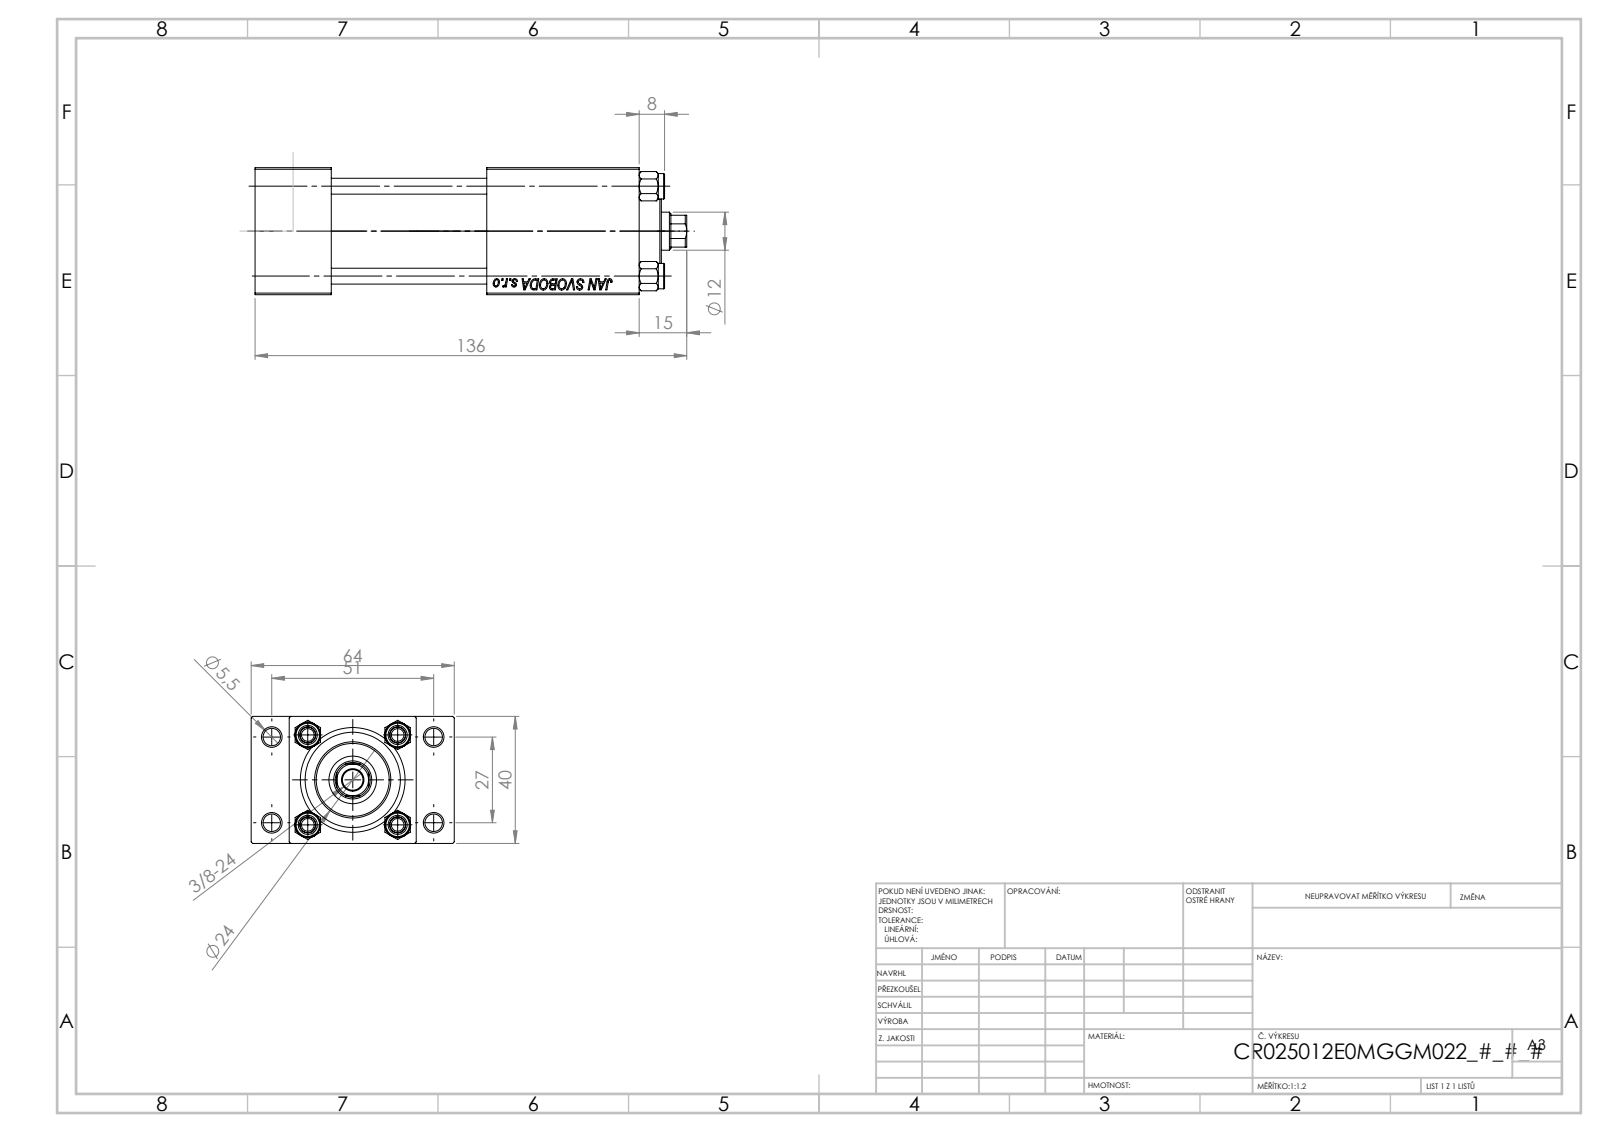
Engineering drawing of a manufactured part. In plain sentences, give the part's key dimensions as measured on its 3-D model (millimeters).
The part is named "V215CR_VCP_E; V215CR_E_Body; V215CR_TYCINKA_E; V215_VC_A (+1 more)". Its 3-D file was written by "SolidWorks 2019 (CONFIG_CONTROL_DESIGN)". It is 11 solids with 1136 faces: 497 planar, 87 cylindrical and 552 other. Overall it measures 136 by 64 by 40 millimeters. Its volume is 164 826 cubic millimeters and its surface area 62 658 square millimeters. Round holes: 4 of diameter 5, 4 of diameter 5.5, 3 of diameter 20, 2 of diameter 7, 2 of diameter 13.16, 1 of diameter 6.5, 1 of diameter 12, 1 of diameter 15, 1 of diameter 25, 1 of diameter 30. Round bosses or shafts: 4 of diameter 8, 1 of diameter 31, 1 of diameter 24. Partial cylindrical surfaces (rounded edges, fillets, slot ends): 1 of radius 5.5. The main face-to-face distances are 40, 24, 12, 52, 121, 97, 92.3, 68.3, 28.7, 64. The hole center spacings are 11.37, 20.01, 28.3, 28.85, 29.89, 39.66, 48.34, 27.
